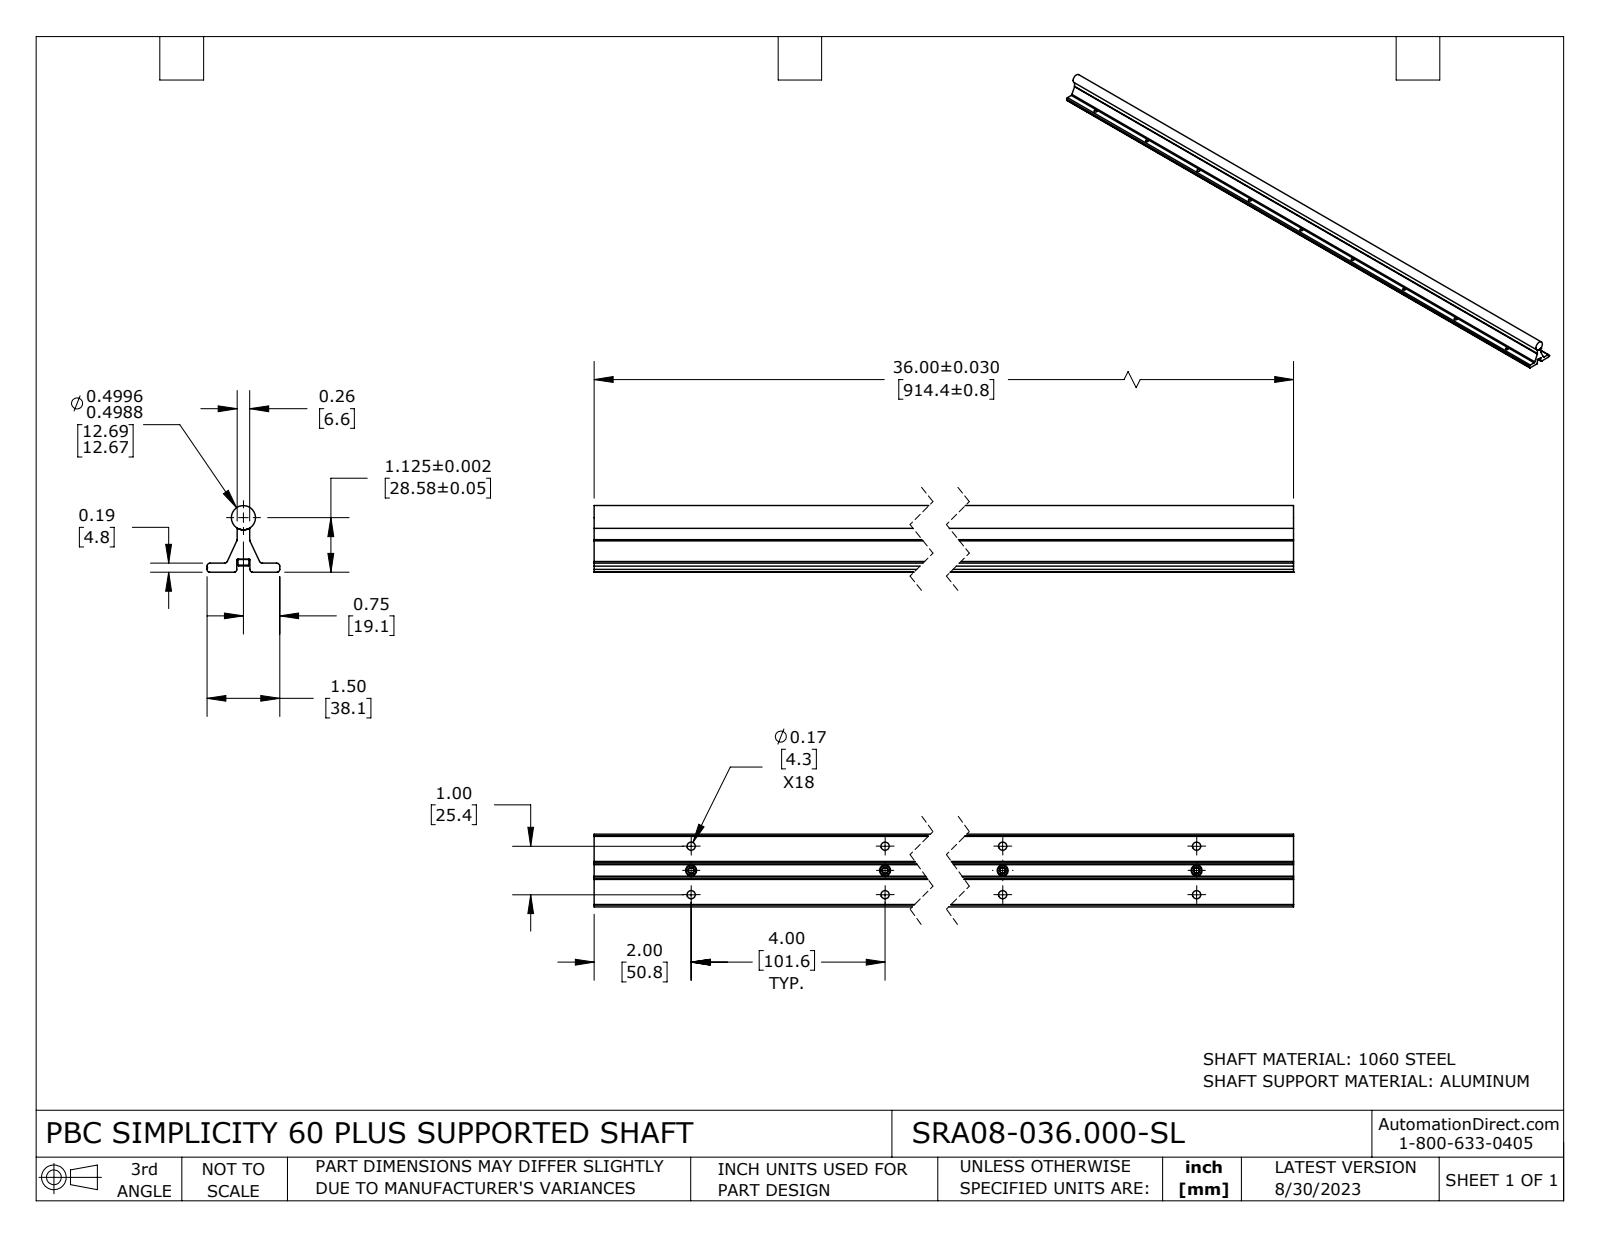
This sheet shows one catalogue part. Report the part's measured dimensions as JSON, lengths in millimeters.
{"part_name": "SRA08-036.000-SL", "step_written_by": "SolidWorks 2021 (CONFIG_CONTROL_DESIGN)", "units": "millimeters", "bodies": {"solids": 11, "faces": 401, "planar": 126, "cylindrical": 140, "other": 135}, "overall_size": [914.4, 38.1, 34.9], "volume_mm3": 402600, "surface_area_mm2": 156600, "round_holes": [[4.3, 27], [2.9, 9], [4, 9]], "round_bosses_or_shafts": [[5.7, 9], [3.5, 9], [12.7, 1]], "partial_cylinders_radius": [[1.5, 8], [0.4, 2], [1.6, 1], [1.6, 1]], "face_to_face_distances": [4.7, 6.9, 6.7, 2.1, 6.6, 15.6, 15.7, 22.4, 22.5, 38.1], "hole_center_spacings": [102.4, 203.6, 101.6, 305.1, 203.2, 406.6, 12.7, 304.8]}
